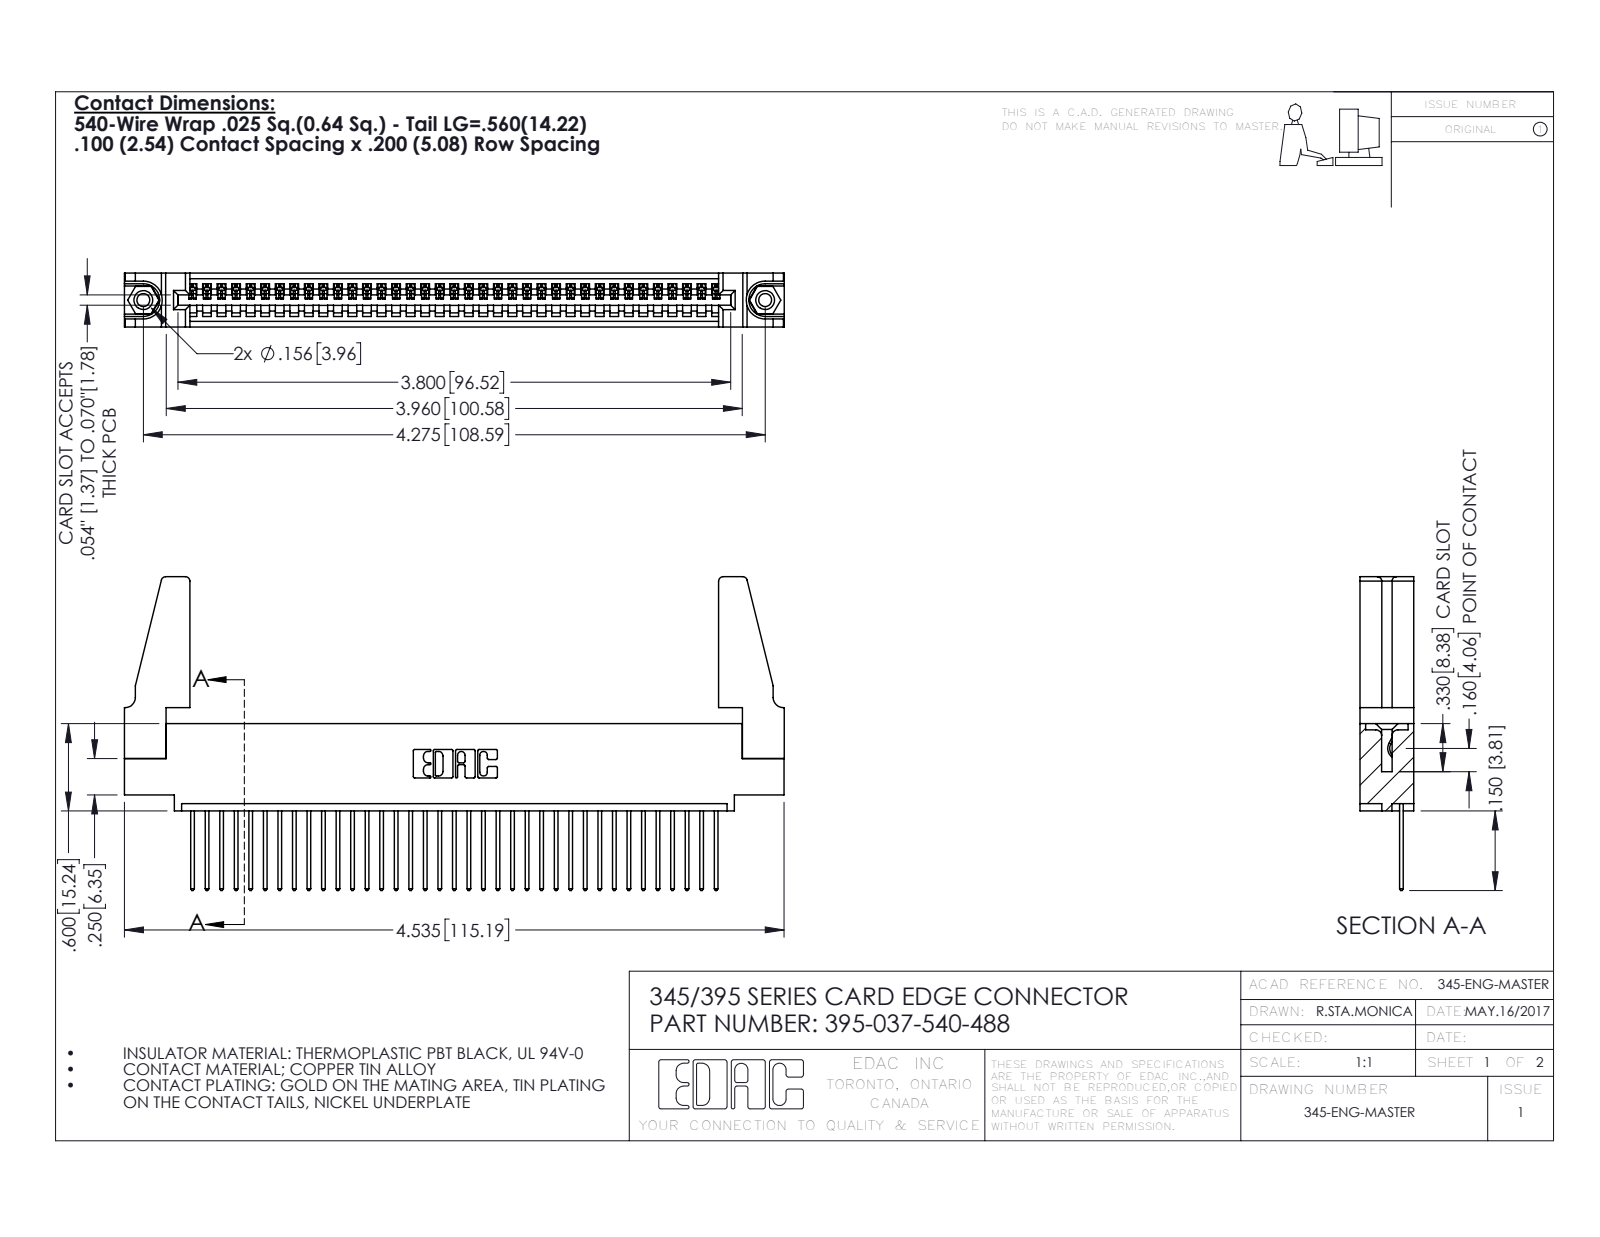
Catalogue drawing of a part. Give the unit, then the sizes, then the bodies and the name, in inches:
Units: inches
Overall size (bounding box): 4.536 × 2.157 × 0.37
Round holes (diameter × count): ⌀0.089 ×2, ⌀0.125 ×2, ⌀0.156 ×2, ⌀0.064 ×1
Round bosses / shafts (diameter × count): ⌀0.155 ×2
Partial cylindrical surfaces — rounded edges, fillets, slot ends (radius × count): R0.006 ×74, R0.01 ×74, R0.01 ×22, R0.03 ×8, R0.007 ×6, R0.031 ×6, R0.026 ×3, R0.031 ×2
Main face-to-face distances: 0.072, 0.298, 0.37, 0.098, 0.272, 0.025, 0.2, 0.225, 0.149, 0.072
Hole centre spacings: 0.27, 4.039, 4.275
Volume: 0.862 in³ · Surface area: 27.84 in²
Bodies: 42 solids, 2400 faces (1636 planar, 748 cylindrical, 16 other)
Part name (STEP PRODUCT): 345-250-001_345-250-001-102; 345-220-078_345-220-088; 345-292-001_345-293-140; 395-037-540-488 (+1 more)
STEP written by: SolidWorks 2016 (CONFIG_CONTROL_DESIGN)
